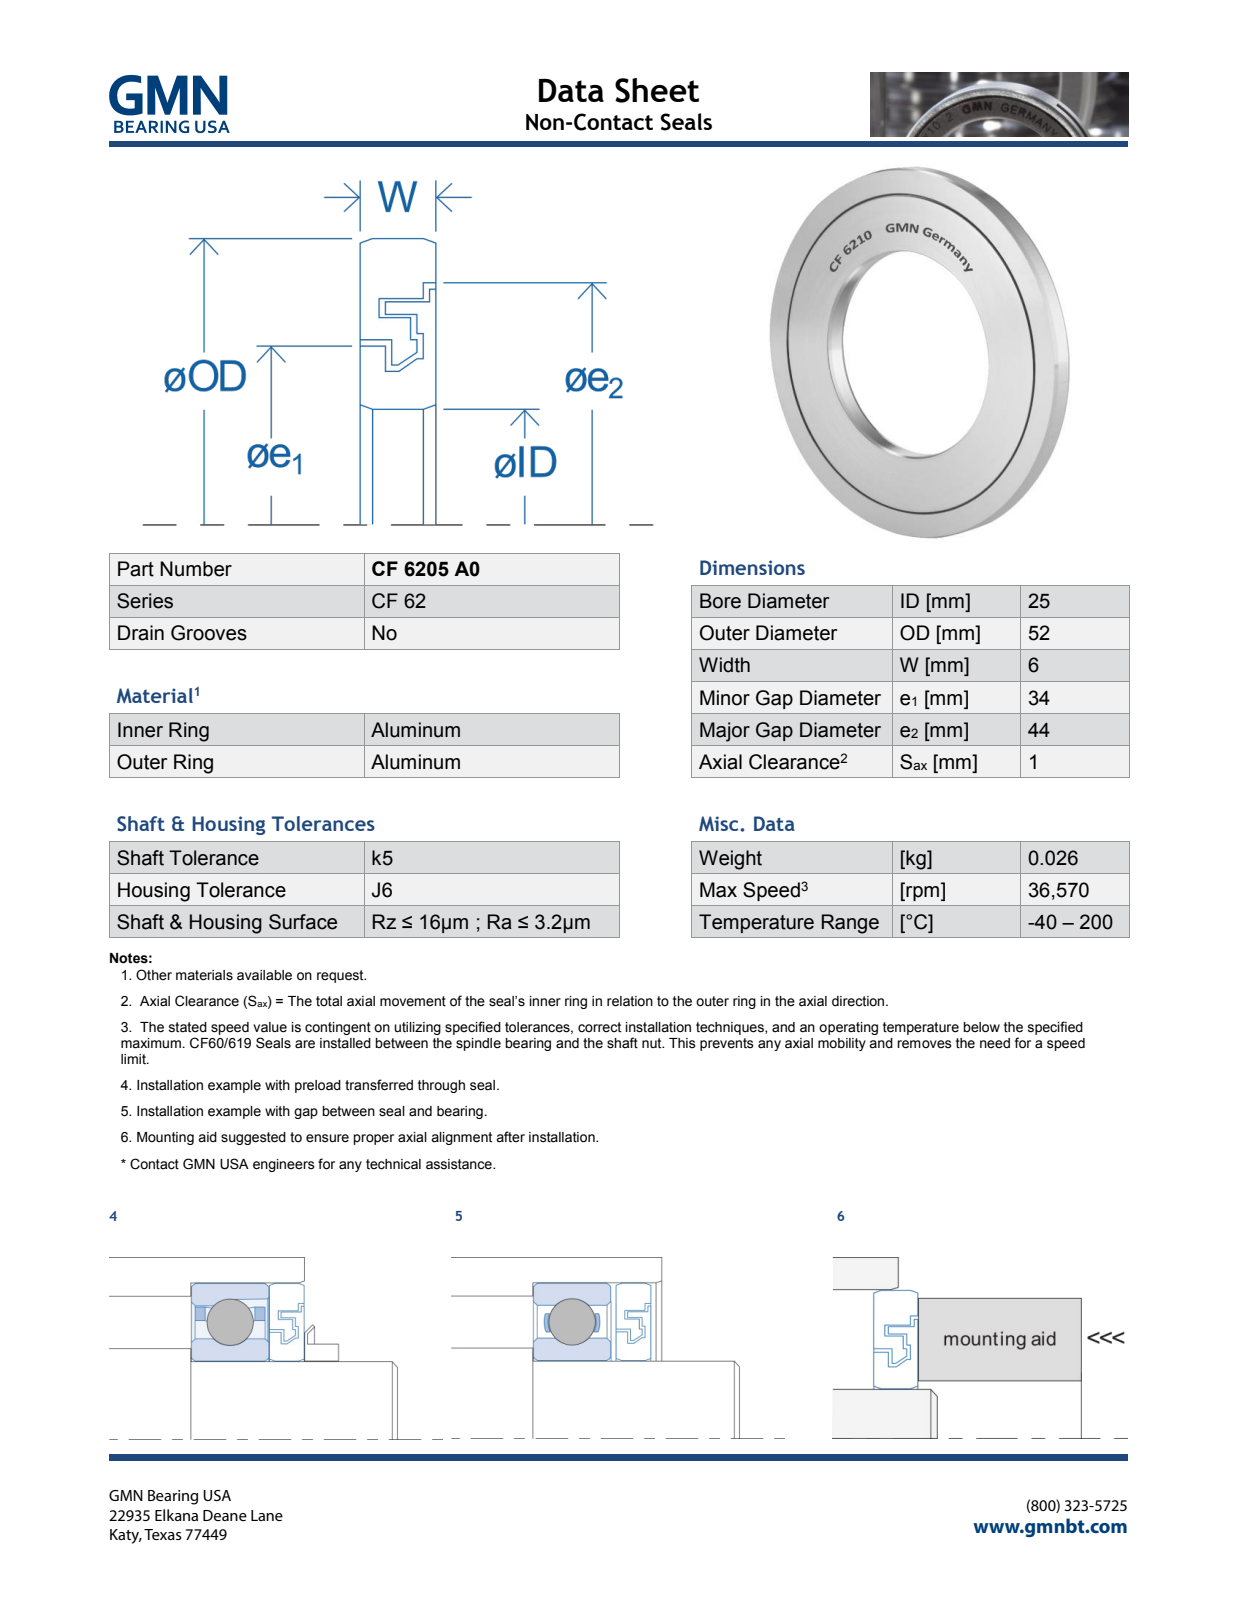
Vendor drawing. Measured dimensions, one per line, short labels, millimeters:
name: CF6205A0_PRT
written by: PRO/ENGINEER BY PARAMETRIC TECHNOLOGY CORPORATION, 2013150 (AUTOMOTIVE_DESIGN)
unit: mm
bodies: 2 solids, 619 faces (577 planar, 30 cylindrical, 12 other)
size: 52 × 52 × 6.05
volume: 8 766 mm³; area: 9 054 mm²
holes: 1× ⌀25, 1× ⌀31, 1× ⌀35, 1× ⌀36, 1× ⌀39, 1× ⌀41.5, 1× ⌀44
bosses: 1× ⌀52, 1× ⌀43, 1× ⌀41, 1× ⌀38.5, 1× ⌀34, 1× ⌀32, 1× ⌀30
face distances: 6, 0.5, 2, 1, 2.5, 1.5, 4, 3, 3.5, 4.5
